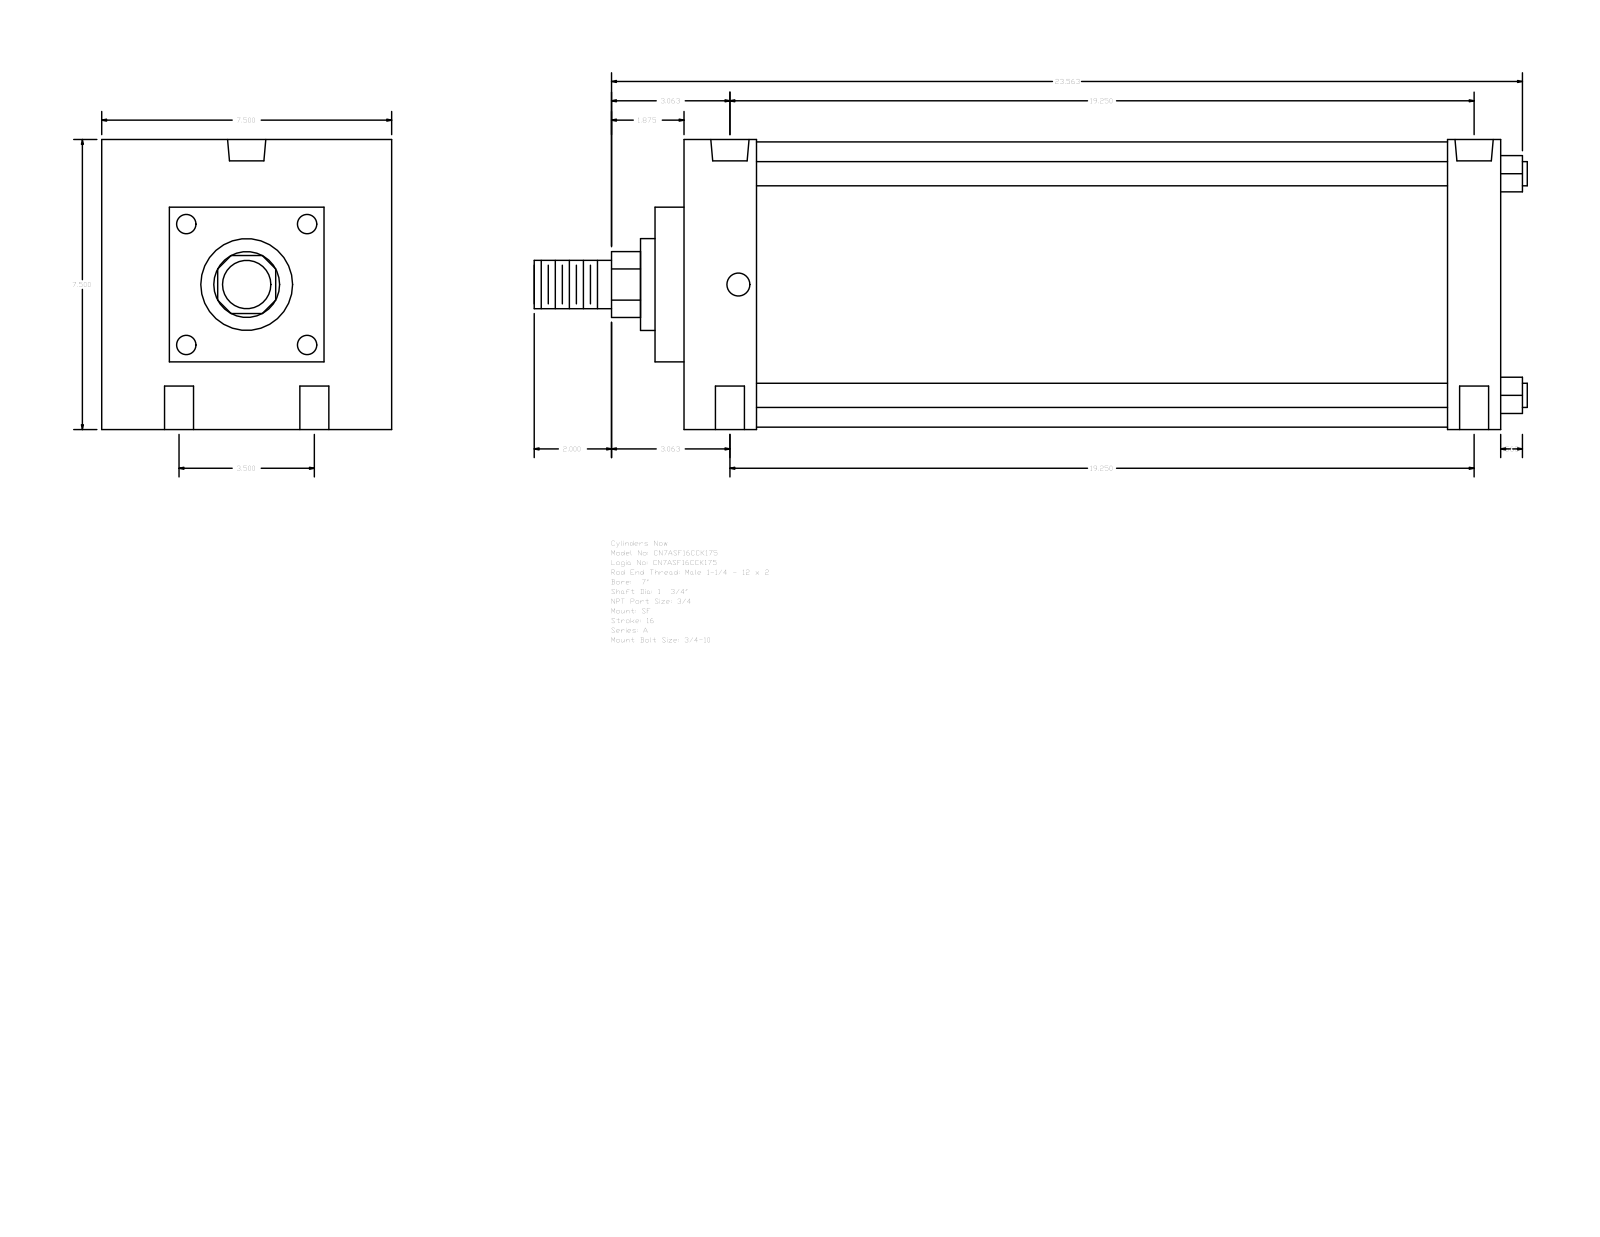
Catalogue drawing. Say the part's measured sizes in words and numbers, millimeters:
The part is named "A_SF__0700_1.75". Its 3-D file was written by "GSSL Pune (CONFIG_CONTROL_DESIGN)". It is 0 solids with 93 faces: 67 planar, 26 cylindrical and 0 other. Overall it measures 652.46 by 190.5 by 190.5 millimeters. Round holes: 4 of diameter 19.05, 2 of diameter 15.08, 2 of diameter 25.12. Round bosses or shafts: 4 of diameter 15.88, 1 of diameter 187.32, 1 of diameter 60.33, 1 of diameter 44.45, 1 of diameter 31.75. Partial cylindrical surfaces (rounded edges, fillets, slot ends): 1 of radius 21.63. The main face-to-face distances are 190.5, 536.58, 146.05, 19.05, 47.63, 501.65, 454.02, 488.95, 34.93, 44.45. The hole center spacings are 44.45, 490.97, 488.95, 88.9, 496.97, 477.83.
